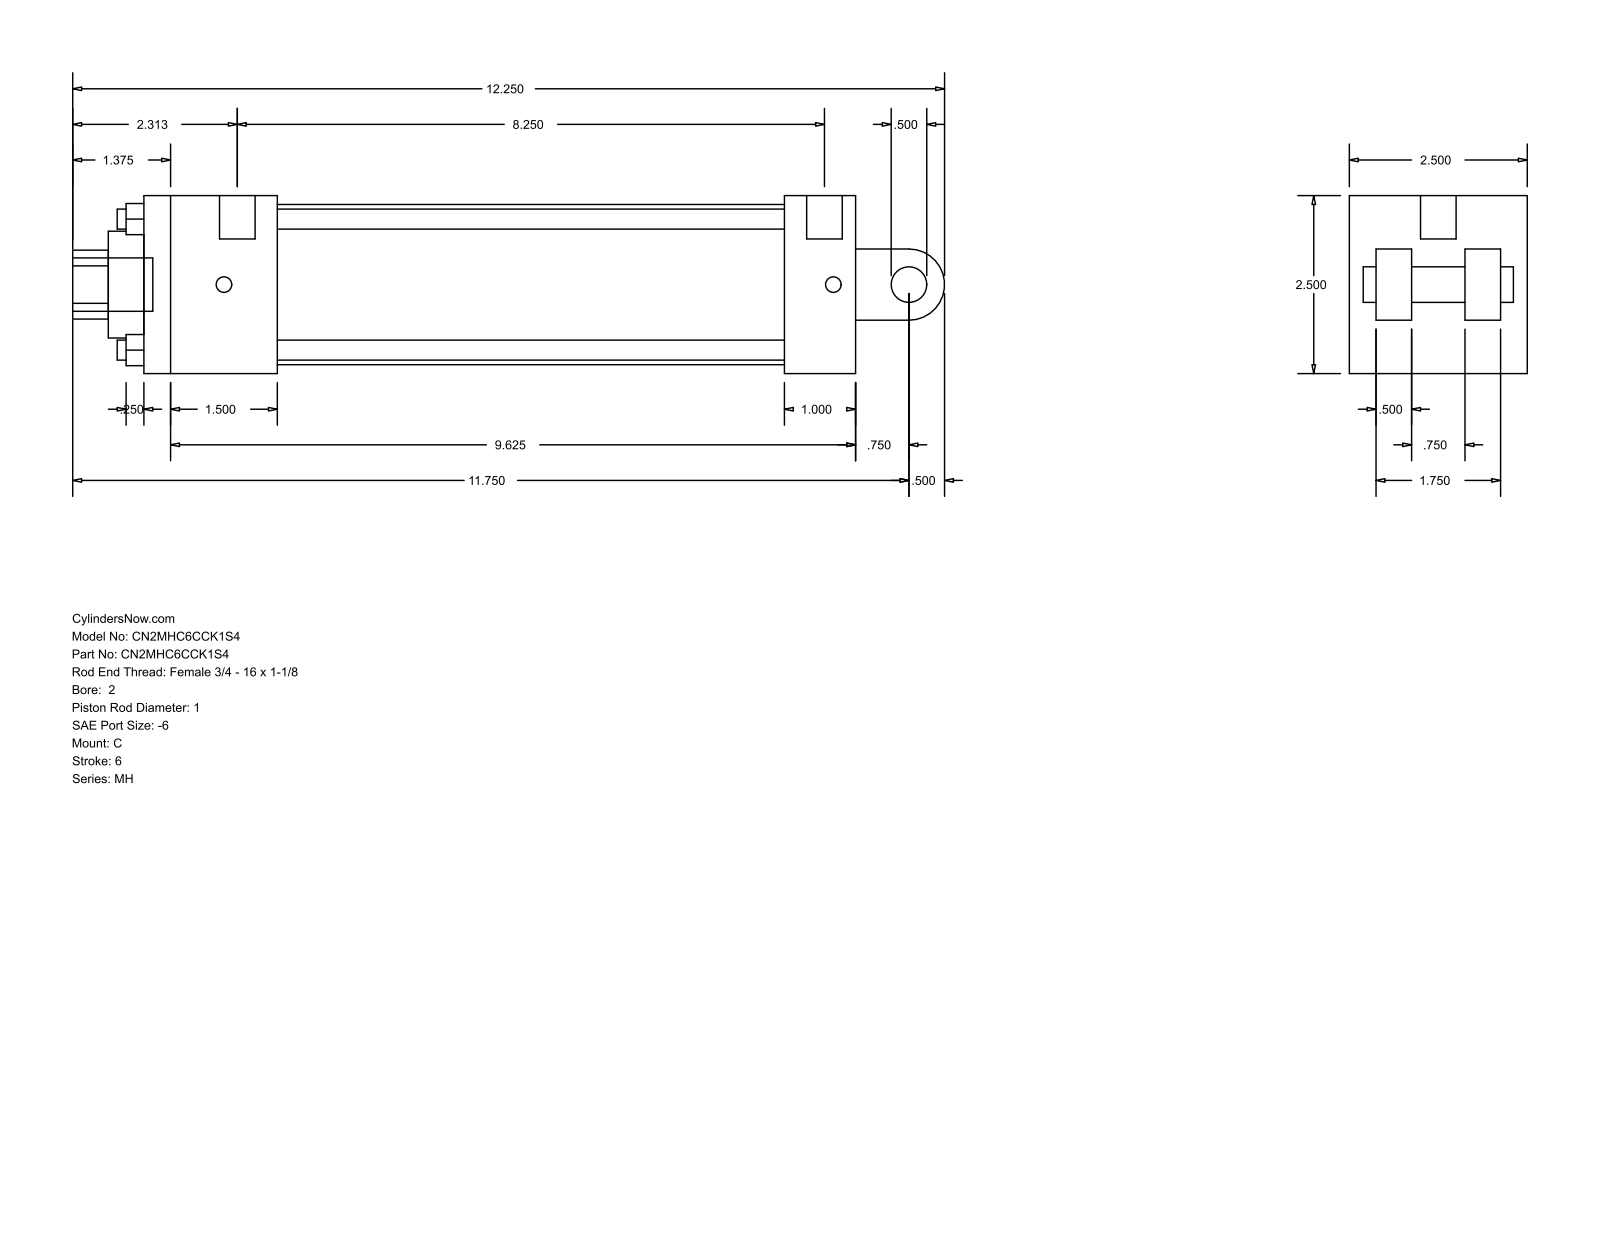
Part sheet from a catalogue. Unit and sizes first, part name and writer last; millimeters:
Units: millimetres
Overall size (bounding box): 311.15 × 63.5 × 63.5
Round holes (diameter × count): ⌀7.14 ×4, ⌀5.56 ×2, ⌀12.7 ×1, ⌀25.4 ×1, ⌀38.1 ×1, ⌀57.15 ×1
Round bosses / shafts (diameter × count): ⌀12.7 ×2, ⌀5.56 ×2, ⌀19.05 ×1
Partial cylindrical surfaces — rounded edges, fillets, slot ends (radius × count): R12.29 ×1, R12.7 ×1
Main face-to-face distances: 63.5, 254, 12.7, 25.4, 9.52, 47.63, 53.98, 228.6, 180.97, 206.37
Hole centre spacings: 33.05, 46.74, 66.1, 3.17
Bodies: 0 solids, 99 faces (70 planar, 29 cylindrical, 0 other)
Part name (STEP PRODUCT): MH_C__0200_1
STEP written by: GSSL Pune (CONFIG_CONTROL_DESIGN)
